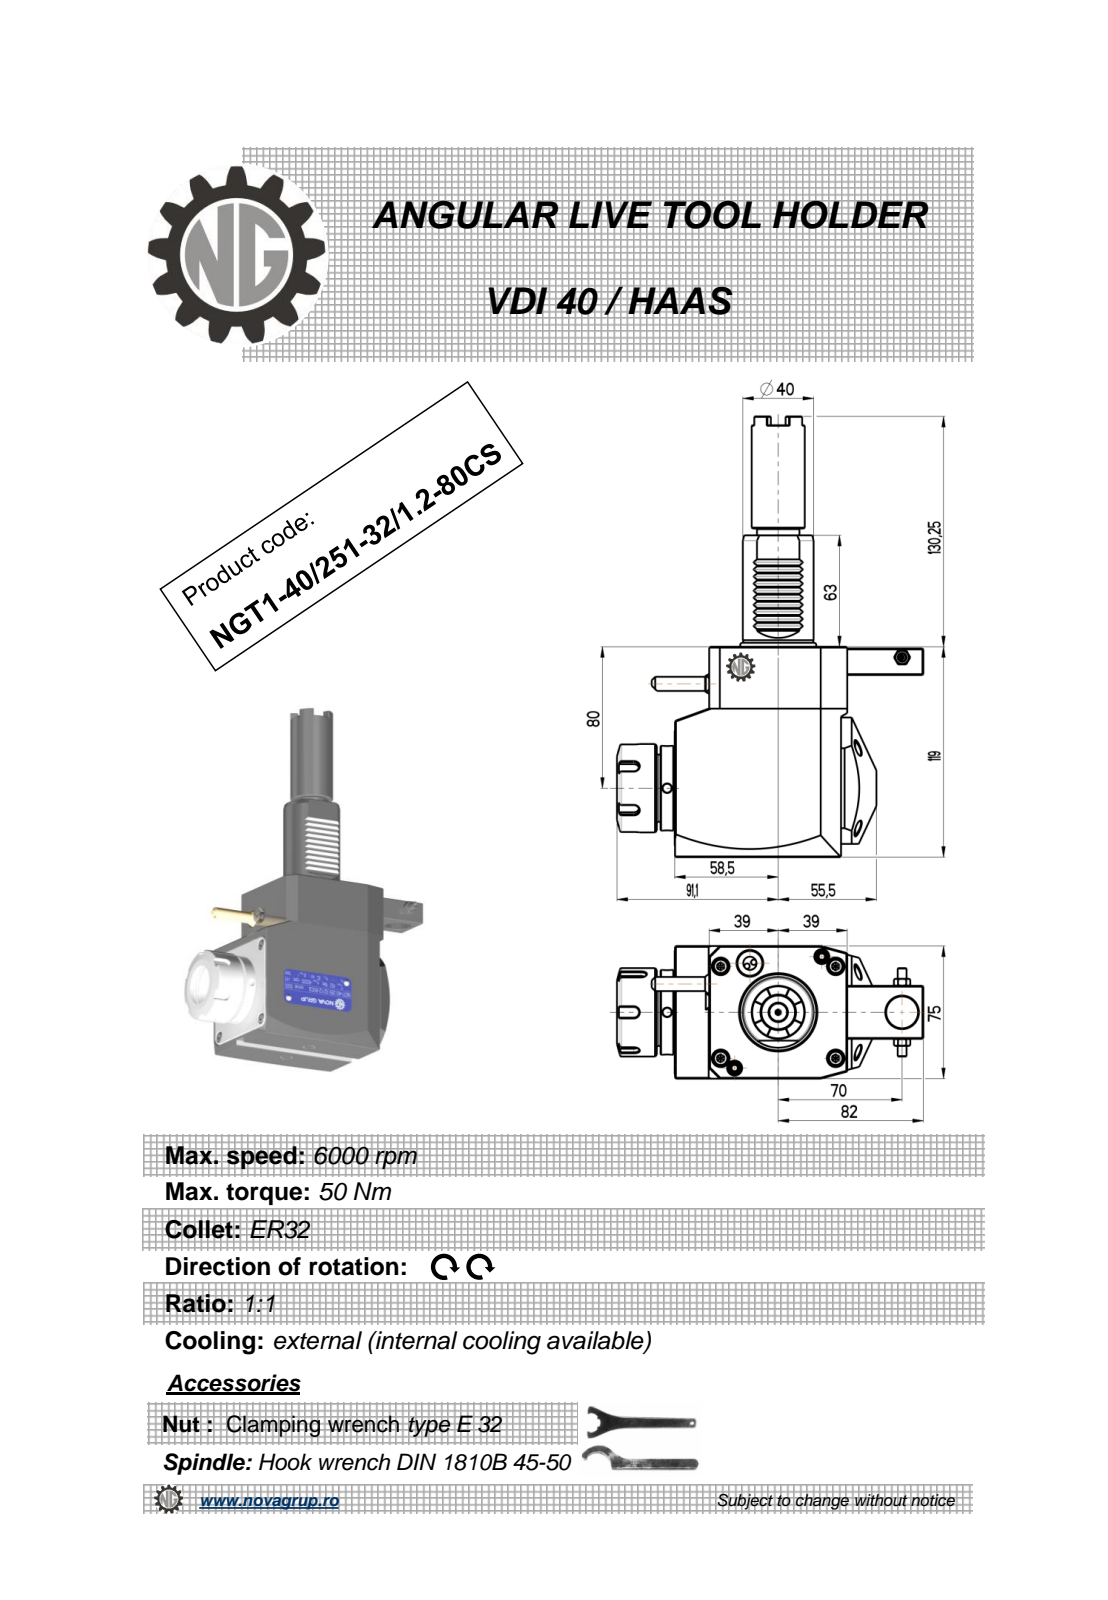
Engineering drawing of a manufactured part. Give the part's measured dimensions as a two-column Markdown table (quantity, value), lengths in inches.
| quantity | value |
| --- | --- |
| part name | NGT1_40_251_32_1_2_80CS |
| STEP written by | PRO/ENGINEER BY PARAMETRIC TECHNOLOGY CORPORATION, 2010280 (CONFIG_CONTROL_DESIGN) |
| units | inches |
| bodies | 1 solid, 481 faces (240 planar, 98 cylindrical, 143 other) |
| overall size | 9.813 × 6.815 × 3.016 |
| volume | 62.43 in³ |
| surface area | 131.1 in² |
| round holes (diameter × count) | 0.197 × 3, 0.118 × 1, 0.165 × 1, 0.374 × 1, 0.709 × 1, 0.768 × 1, 1.063 × 1 |
| round bosses / shafts (diameter × count) | 1.969 × 1, 1.89 × 1, 1.634 × 1, 1.614 × 1, 1.575 × 1, 1.181 × 1, 0.945 × 1, 0.394 × 1 |
| partial cylindrical surfaces (radius × count) | 0.01 × 12, 0.012 × 10, 0.008 × 6, 0.118 × 5, 0.228 × 2, 0.236 × 2, 23.622 × 2, 0.02 × 1 |
| main face-to-face distances | 2.953, 4.685, 0.768, 3.839, 3.071, 0.039, 0.886, 0.138, 0.787, 4.488 |
| hole center spacings | 0.824, 2.407, 2.47, 2.756, 2.854, 5.226, 5.983 |
